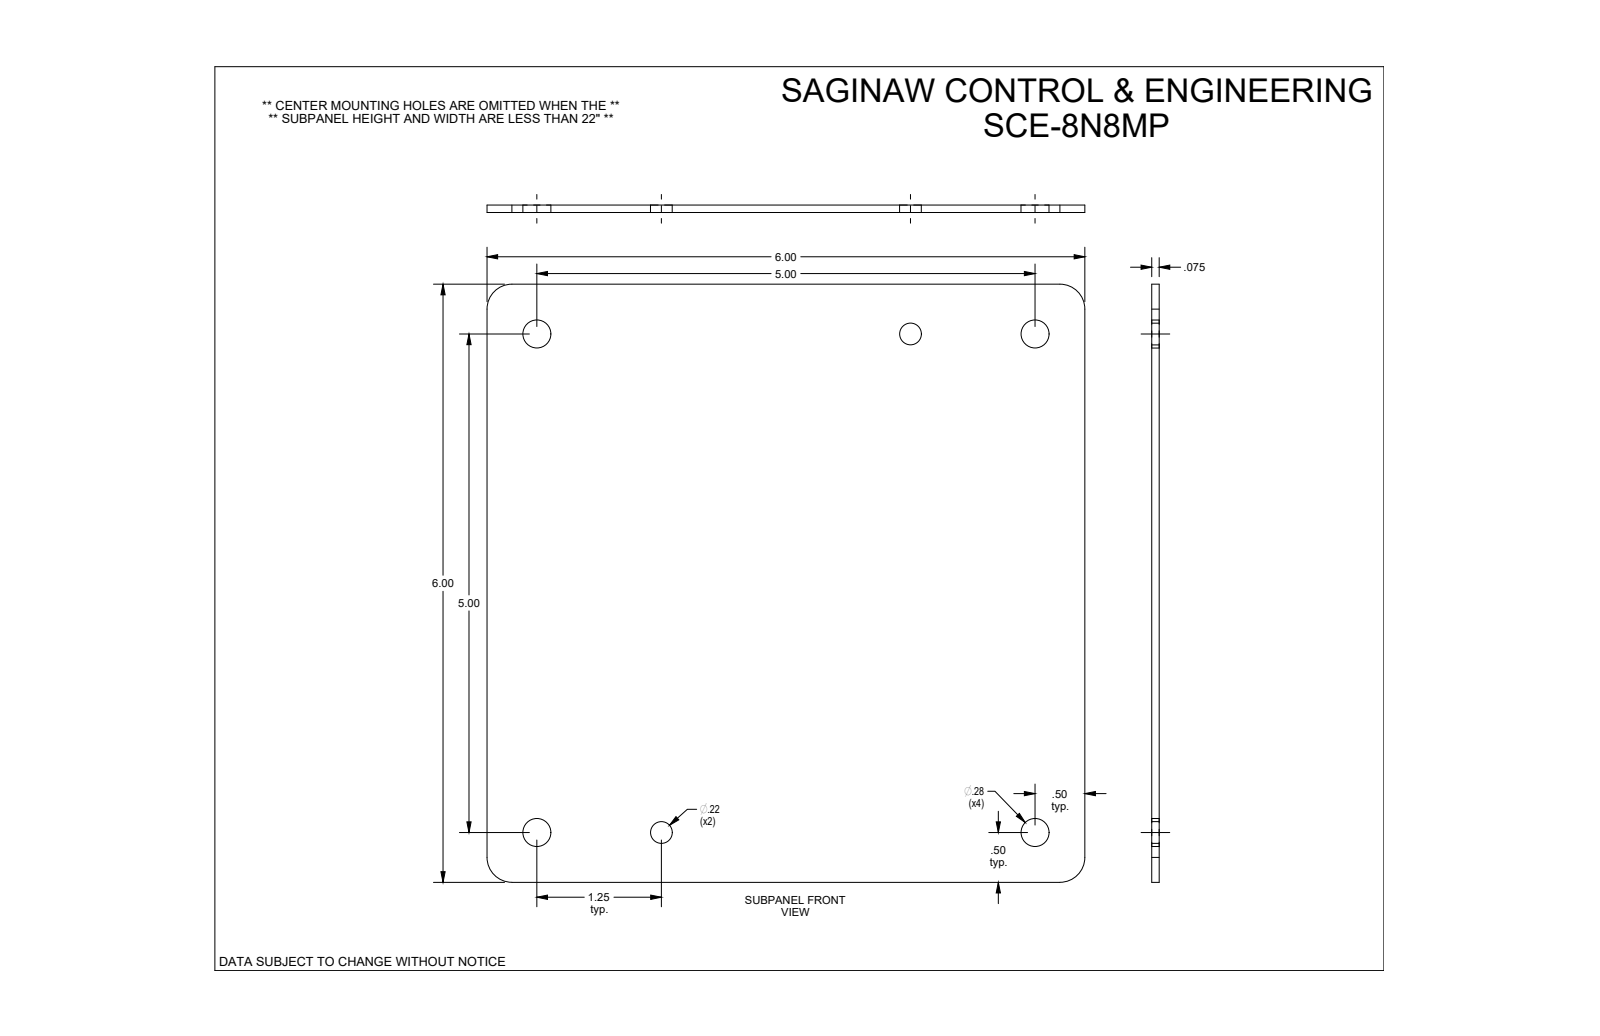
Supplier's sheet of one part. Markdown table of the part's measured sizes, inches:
| quantity | value |
| --- | --- |
| part name | SCE-8N8MP |
| STEP written by | SolidWorks 2019 (CONFIG_CONTROL_DESIGN) |
| units | inches |
| bodies | 1 solid, 16 faces (6 planar, 10 cylindrical, 0 other) |
| overall size | 6 × 6 × 0.075 |
| volume | 2.672 in³ |
| surface area | 73.38 in² |
| round holes (diameter × count) | 0.281 × 4, 0.218 × 2 |
| partial cylindrical surfaces (radius × count) | 0.25 × 4 |
| main face-to-face distances | 0.075, 6 |
| hole center spacings | 5, 1.25, 3.75, 5.154, 6.25, 7.071, 5.59 |
